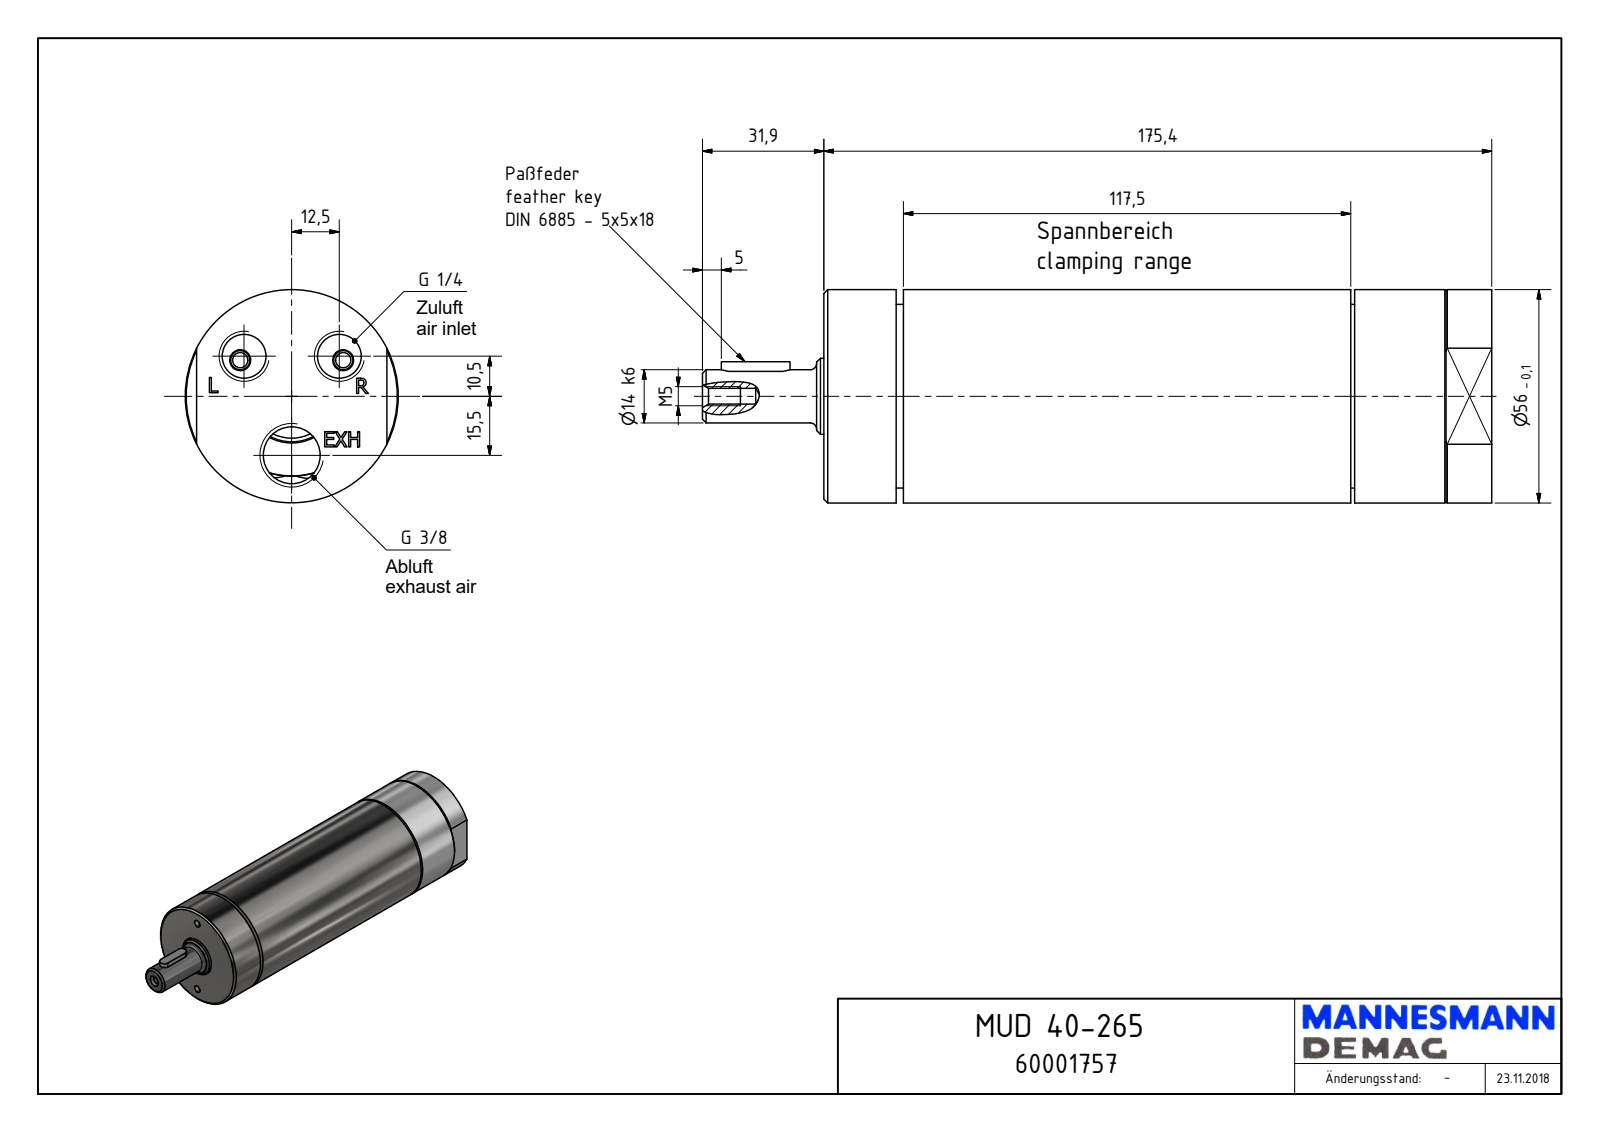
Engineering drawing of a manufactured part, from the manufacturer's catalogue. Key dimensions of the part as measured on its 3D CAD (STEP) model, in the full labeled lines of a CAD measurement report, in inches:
Part name (STEP PRODUCT): MUD 40-265_60001757
STEP written by: Autodesk Inventor 2018 (AUTOMOTIVE_DESIGN)
Units: inches
Bodies: 1 solid, 186 faces (103 planar, 42 cylindrical, 41 other)
Overall size (bounding box): 8.161 × 2.205 × 2.205
Volume: 26.2 in³ · Surface area: 78.11 in²
Round holes (diameter × count): ⌀0.157 ×2, ⌀0.451 ×2, ⌀0.163 ×1, ⌀0.589 ×1, ⌀0.827 ×1, ⌀0.837 ×1, ⌀0.927 ×1, ⌀1.024 ×1, ⌀1.905 ×1
Round bosses / shafts (diameter × count): ⌀2.205 ×1, ⌀1.897 ×1, ⌀0.785 ×1, ⌀0.551 ×1
Partial cylindrical surfaces — rounded edges, fillets, slot ends (radius × count): R0.394 ×6, R0.098 ×2, R0.236 ×2, R0.846 ×1, R0.871 ×1, R0.906 ×1
Main face-to-face distances: 6.906, 0.823, 5.449, 1.457, 4.626, 6.083, 0.075, 5.488, 0.748, 4.701
Hole centre spacings: 0.643, 0.827, 1.136, 1.334, 0.217, 0.61, 0.984, 1.437
